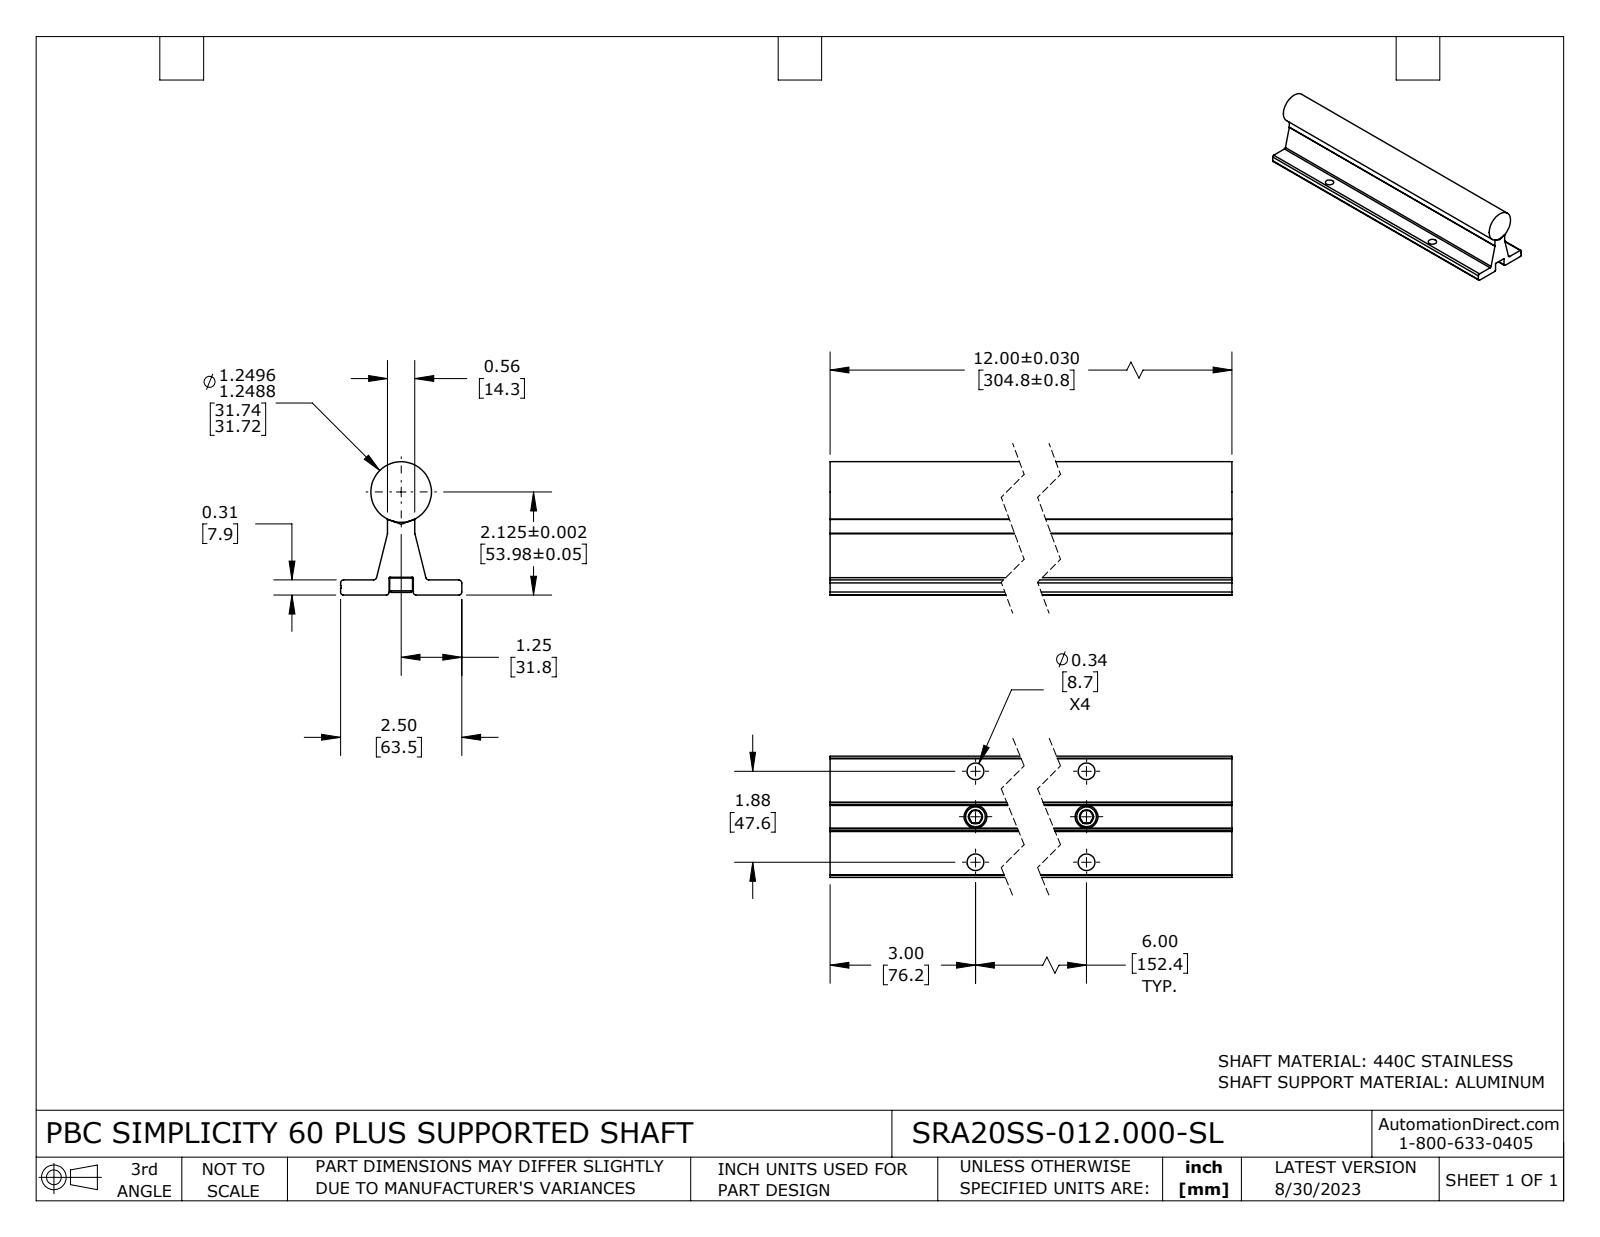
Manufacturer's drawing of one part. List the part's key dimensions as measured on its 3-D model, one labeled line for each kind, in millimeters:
Part name (STEP PRODUCT): SRA20SS-012.000-SL
STEP written by: SolidWorks 2021 (CONFIG_CONTROL_DESIGN)
Units: millimetres
Bodies: 4 solids, 123 faces (49 planar, 44 cylindrical, 30 other)
Overall size (bounding box): 304.8 × 69.9 × 63.5
Volume: 533 900 mm³ · Surface area: 104 200 mm²
Round holes (diameter × count): ⌀8.7 ×6, ⌀6.9 ×2, ⌀9.5 ×2
Round bosses / shafts (diameter × count): ⌀11.9 ×2, ⌀8 ×2, ⌀31.8 ×1
Partial cylindrical surfaces — rounded edges, fillets, slot ends (radius × count): R1.6 ×6, R1.6 ×3, R0.4 ×2, R0.8 ×2, R1.6 ×1
Main face-to-face distances: 8, 0.8, 13.5, 9.3, 1.4, 24.6, 25.4, 38.1, 38.9, 12.7
Hole centre spacings: 23.8, 154.3, 152.4, 47.6, 159.7
